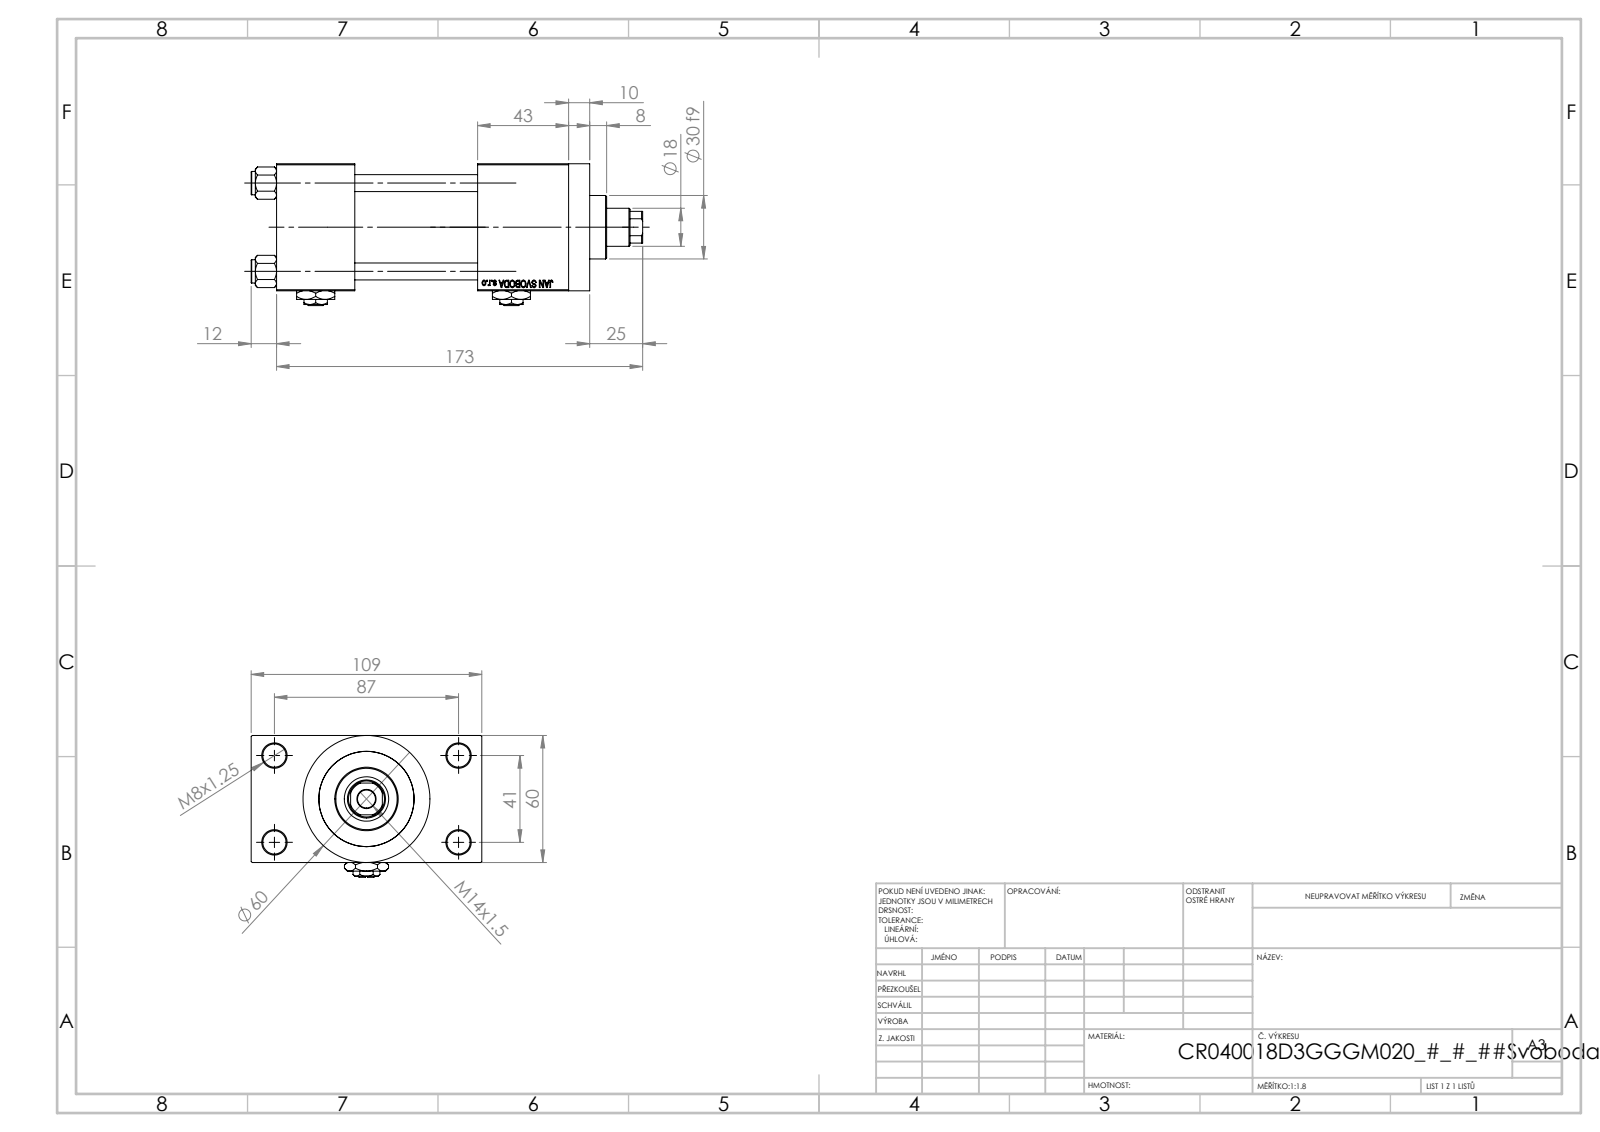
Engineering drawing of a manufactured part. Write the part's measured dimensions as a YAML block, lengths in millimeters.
part_name: "Zatka_pro_OIL_PORT; V215CR_VCP_D; V215_VC_A; V215CR_D_TYCINKA (+2 more)"
step_written_by: "SolidWorks 2019 (CONFIG_CONTROL_DESIGN)"
units: millimeters
bodies: {solids: 13, faces: 1206, planar: 546, cylindrical: 100, other: 560}
overall_size: [185, 109, 67]
volume: 515592
surface_area: 123915
round_holes:
  - {diameter: 8, count: 4}
  - {diameter: 11, count: 4}
  - {diameter: 7, count: 2}
  - {diameter: 16.66, count: 2}
  - {diameter: 24, count: 2}
  - {diameter: 8.5, count: 1}
  - {diameter: 18, count: 1}
  - {diameter: 21, count: 1}
  - {diameter: 31, count: 1}
  - {diameter: 40, count: 1}
  - {diameter: 45, count: 1}
round_bosses_or_shafts:
  - {diameter: 11, count: 4}
  - {diameter: 60, count: 1}
  - {diameter: 46, count: 1}
  - {diameter: 30, count: 1}
partial_cylinders:
  - {radius: 8.5, count: 1}
face_to_face_distances: [60, 24.5, 84.5, 58, 37, 95, 43, 138, 101, 109]
hole_center_spacings: [22.65, 29.49, 41.7, 47.15, 48.09, 64.35, 76.49, 41]
